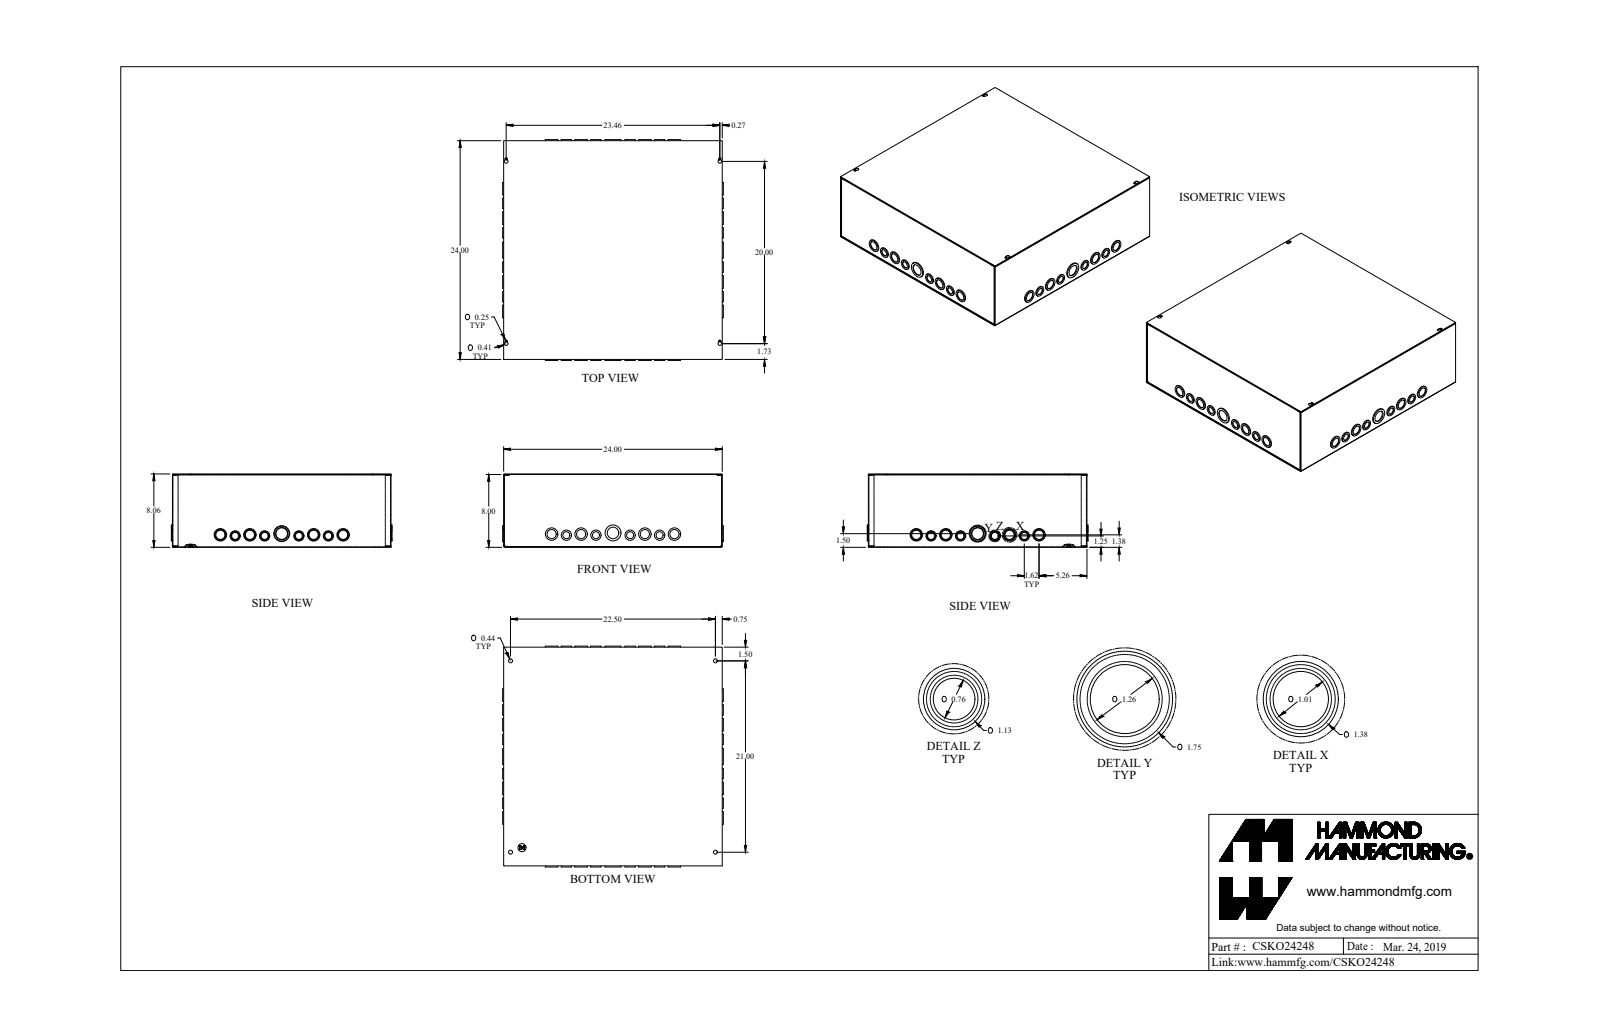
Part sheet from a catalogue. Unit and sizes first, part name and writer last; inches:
Units: inches
Overall size (bounding box): 24.234 × 24.234 × 8.057
Round holes (diameter × count): ⌀1.011 ×16, ⌀1.261 ×10, ⌀0.761 ×8, ⌀0.17 ×5, ⌀0.437 ×4, ⌀1.636 ×2, ⌀0.5 ×1
Round bosses / shafts (diameter × count): ⌀1.125 ×14, ⌀1.375 ×9, ⌀0.875 ×8, ⌀0.875 ×6, ⌀1.125 ×4, ⌀1.75 ×2, ⌀1.375 ×1, ⌀0.492 ×1
Partial cylindrical surfaces — rounded edges, fillets, slot ends (radius × count): R0.029 ×12, R0.086 ×12, R0.057 ×8, R0.125 ×4, R0.203 ×4
Main face-to-face distances: 0.057, 8, 23.943, 7.943, 8.057, 24, 23.886, 0.114, 0.08, 7.863
Hole centre spacings: 1.625, 3.24, 8.621, 7, 10.24, 0.693, 1.896, 3.502
Volume: 114.8 in³ · Surface area: 4 050 in²
Bodies: 4 solids, 637 faces (269 planar, 360 cylindrical, 8 other)
Part name (STEP PRODUCT): CSKO24248_Default
STEP written by: SolidWorks 2019 (CONFIG_CONTROL_DESIGN)
